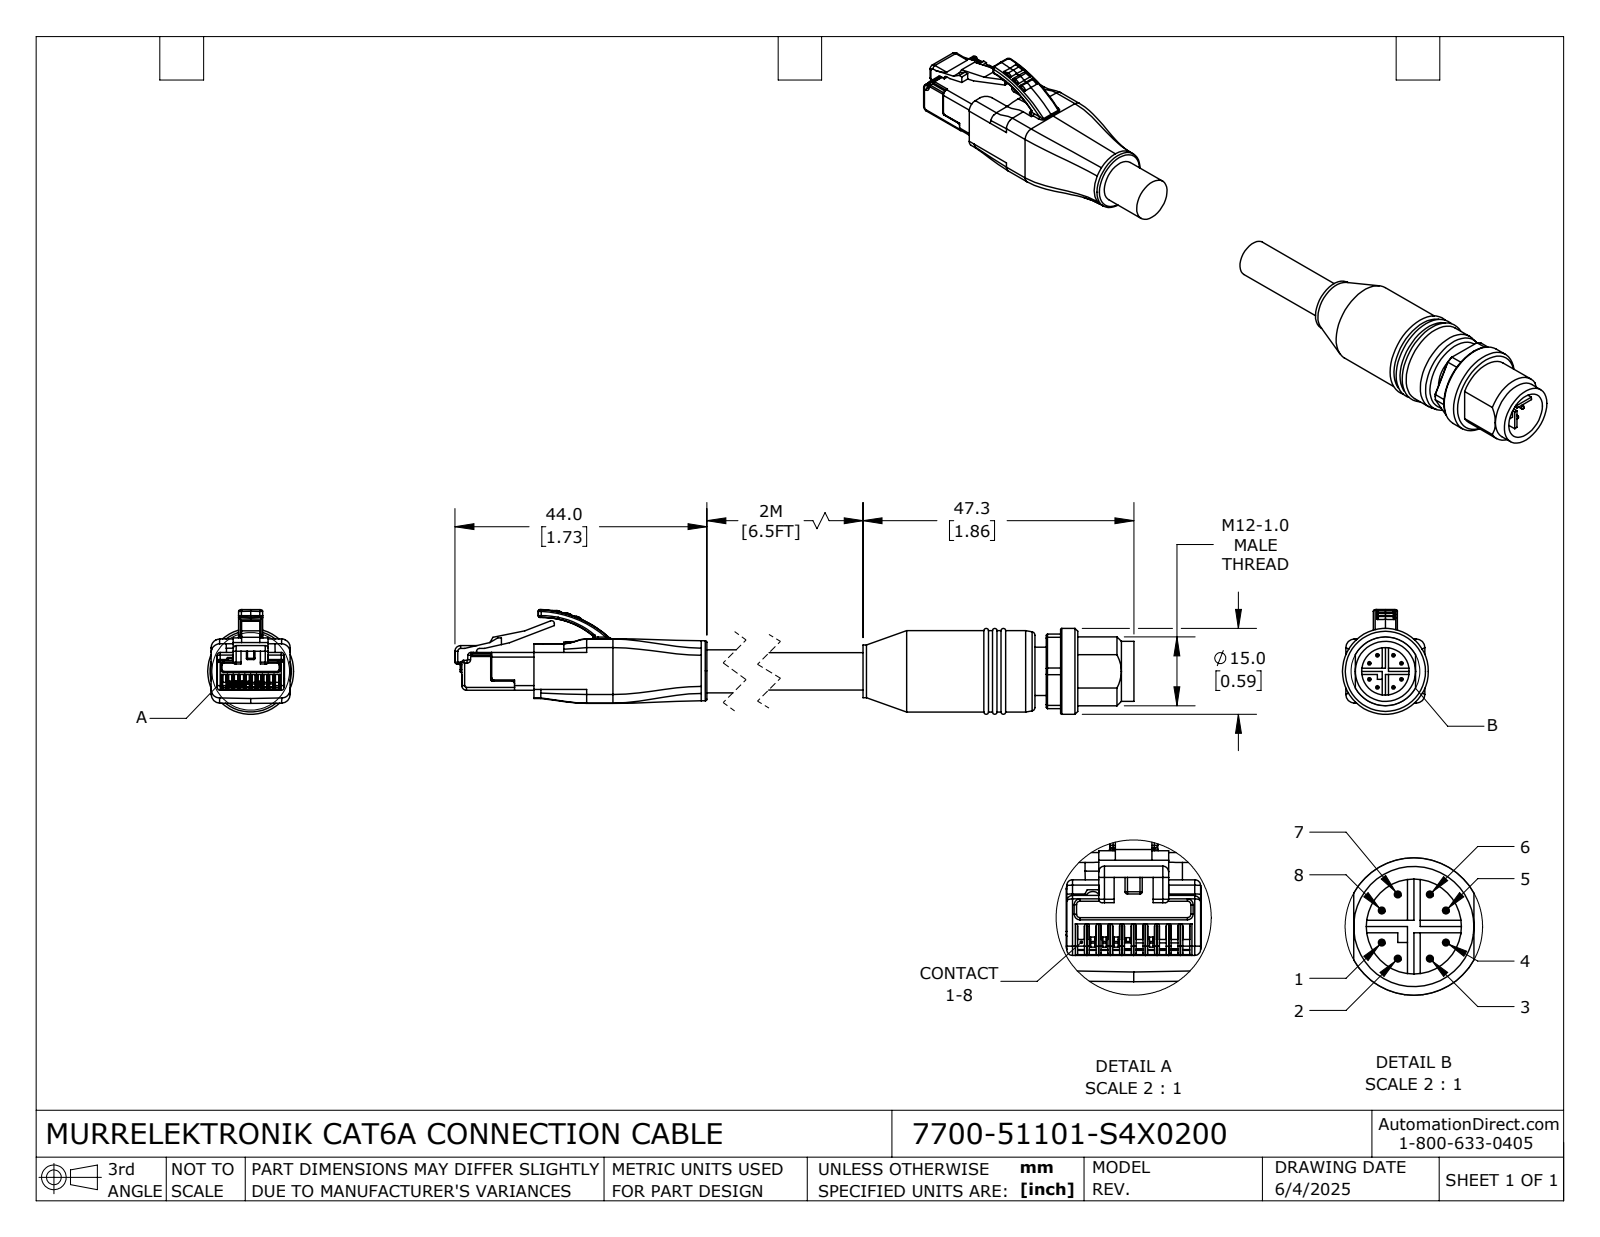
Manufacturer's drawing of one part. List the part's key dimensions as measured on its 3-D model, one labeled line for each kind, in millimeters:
Part name (STEP PRODUCT): 7700-51101-S4X0200_RJ45; 7700-51101-S4X0200; 7700-51101-S4X0200_MALE
STEP written by: SolidWorks 2024 (CONFIG_CONTROL_DESIGN)
Units: millimetres
Bodies: 2 solids, 752 faces (352 planar, 226 cylindrical, 174 other)
Overall size (bounding box): 144.3 × 18.29 × 15
Volume: 11 935 mm³ · Surface area: 5 963 mm²
Round holes (diameter × count): ⌀8.3 ×1
Round bosses / shafts (diameter × count): ⌀0.6 ×8, ⌀10.5 ×2, ⌀15 ×1, ⌀14.2 ×1, ⌀9.2 ×1, ⌀8.4 ×1, ⌀7.5 ×1, ⌀6.5 ×1
Partial cylindrical surfaces — rounded edges, fillets, slot ends (radius × count): R0.2 ×61, R0.5 ×25, R0.3 ×14, R1.5 ×9, R0.8 ×5, R0.54 ×2, R5 ×2, R0.13 ×1
Main face-to-face distances: 13.8, 3.85, 4.7, 2, 1.65, 12.15, 6.35, 7.45, 5.8, 2.75
